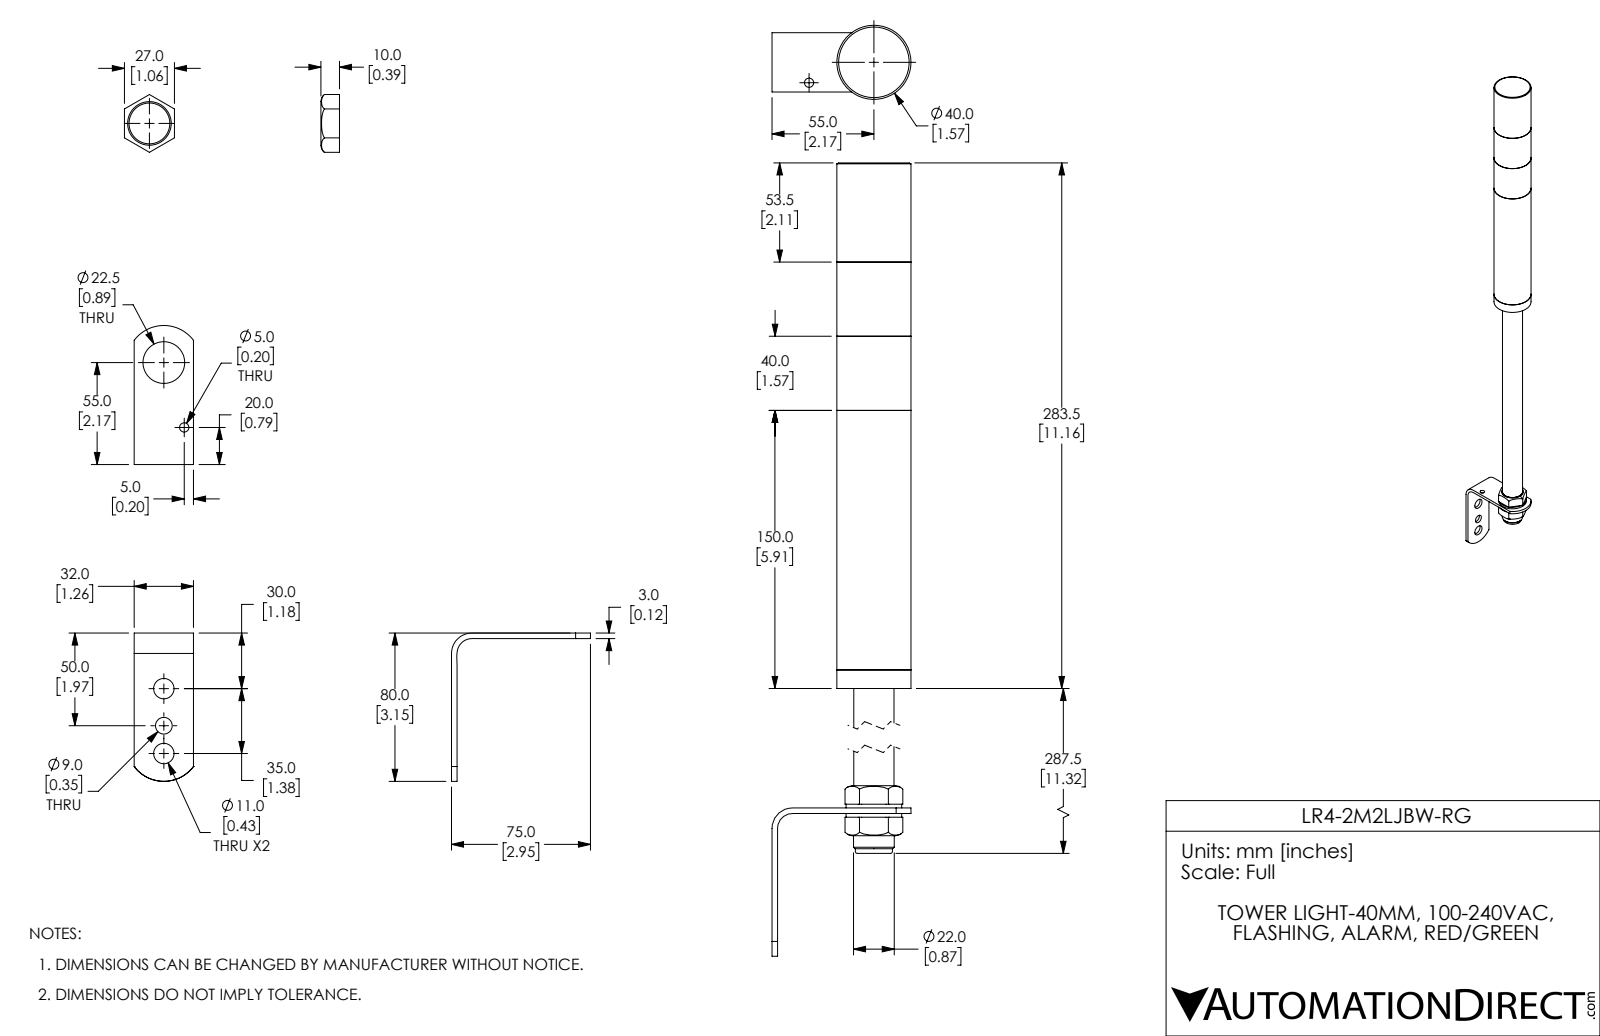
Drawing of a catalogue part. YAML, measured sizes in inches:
part_name: "LR4-2M2LJBW-RG"
step_written_by: "SolidWorks 2017 (AUTOMOTIVE_DESIGN)"
units: inches
bodies: {solids: 11, faces: 143, planar: 52, cylindrical: 77, other: 14}
overall_size: [24.665, 2.953, 1.575]
volume: 25.69
surface_area: 179.5
round_holes:
  - {diameter: 0.126, count: 2}
  - {diameter: 0.433, count: 2}
  - {diameter: 0.197, count: 1}
  - {diameter: 0.303, count: 1}
  - {diameter: 0.354, count: 1}
  - {diameter: 0.697, count: 1}
  - {diameter: 0.866, count: 1}
  - {diameter: 0.886, count: 1}
  - {diameter: 1.087, count: 1}
  - {diameter: 1.386, count: 1}
  - {diameter: 1.39, count: 1}
  - {diameter: 1.463, count: 1}
round_bosses_or_shafts:
  - {diameter: 1.575, count: 1}
  - {diameter: 1.461, count: 1}
  - {diameter: 1.366, count: 1}
  - {diameter: 1.181, count: 1}
  - {diameter: 0.854, count: 1}
partial_cylinders:
  - {radius: 0.787, count: 1}
face_to_face_distances: [1.575, 3.15, 5.354, 6.929, 1.701, 3.276, 0.197, 10.205, 4.85, 8.516]
hole_center_spacings: [0.283, 0.567, 0.591, 0.787, 1.177, 1.378, 1.444, 1.717]
